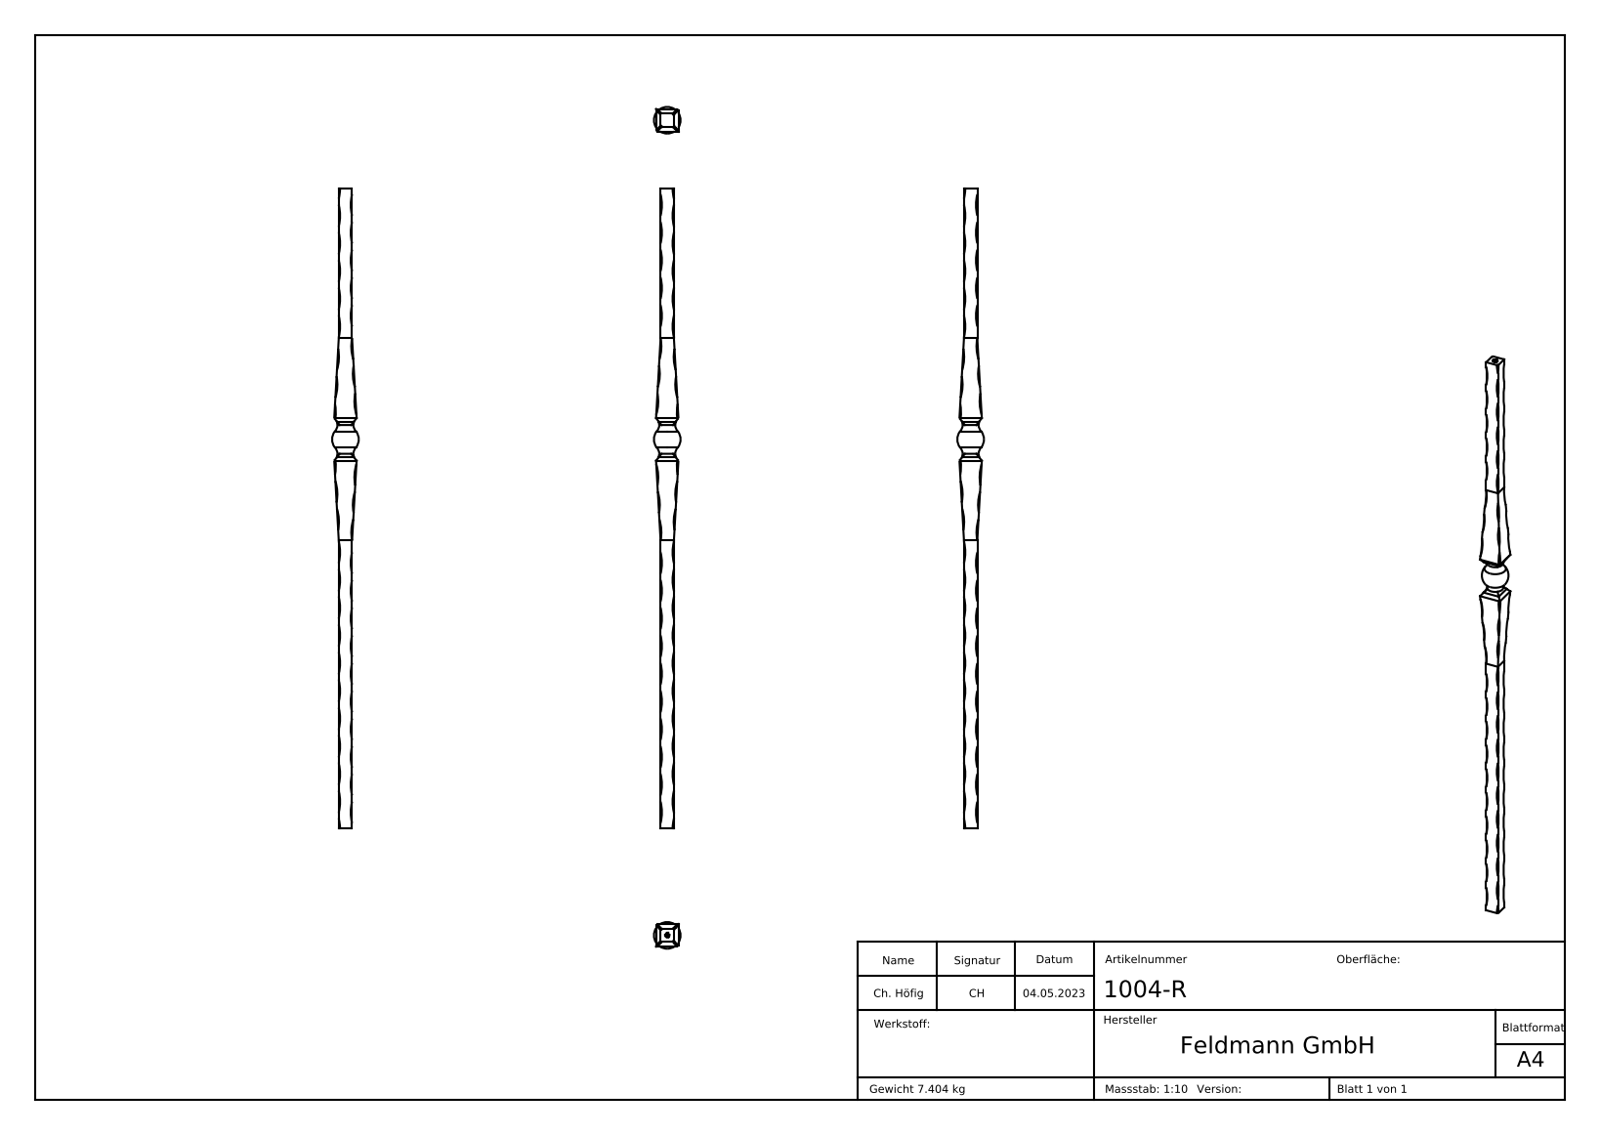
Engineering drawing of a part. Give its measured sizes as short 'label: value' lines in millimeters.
name: 1004-R
written by: SolidWorks 2018 (CONFIG_CONTROL_DESIGN)
unit: mm
bodies: 1 solid, 348 faces (158 planar, 0 cylindrical, 190 other)
size: 1200 × 50 × 50
volume: 949 227 mm³; area: 132 656 mm²
face distances: 25, 46.44, 15.5, 1200, 1199.9, 1.84, 3.27, 1.96, 4.39, 1.82
